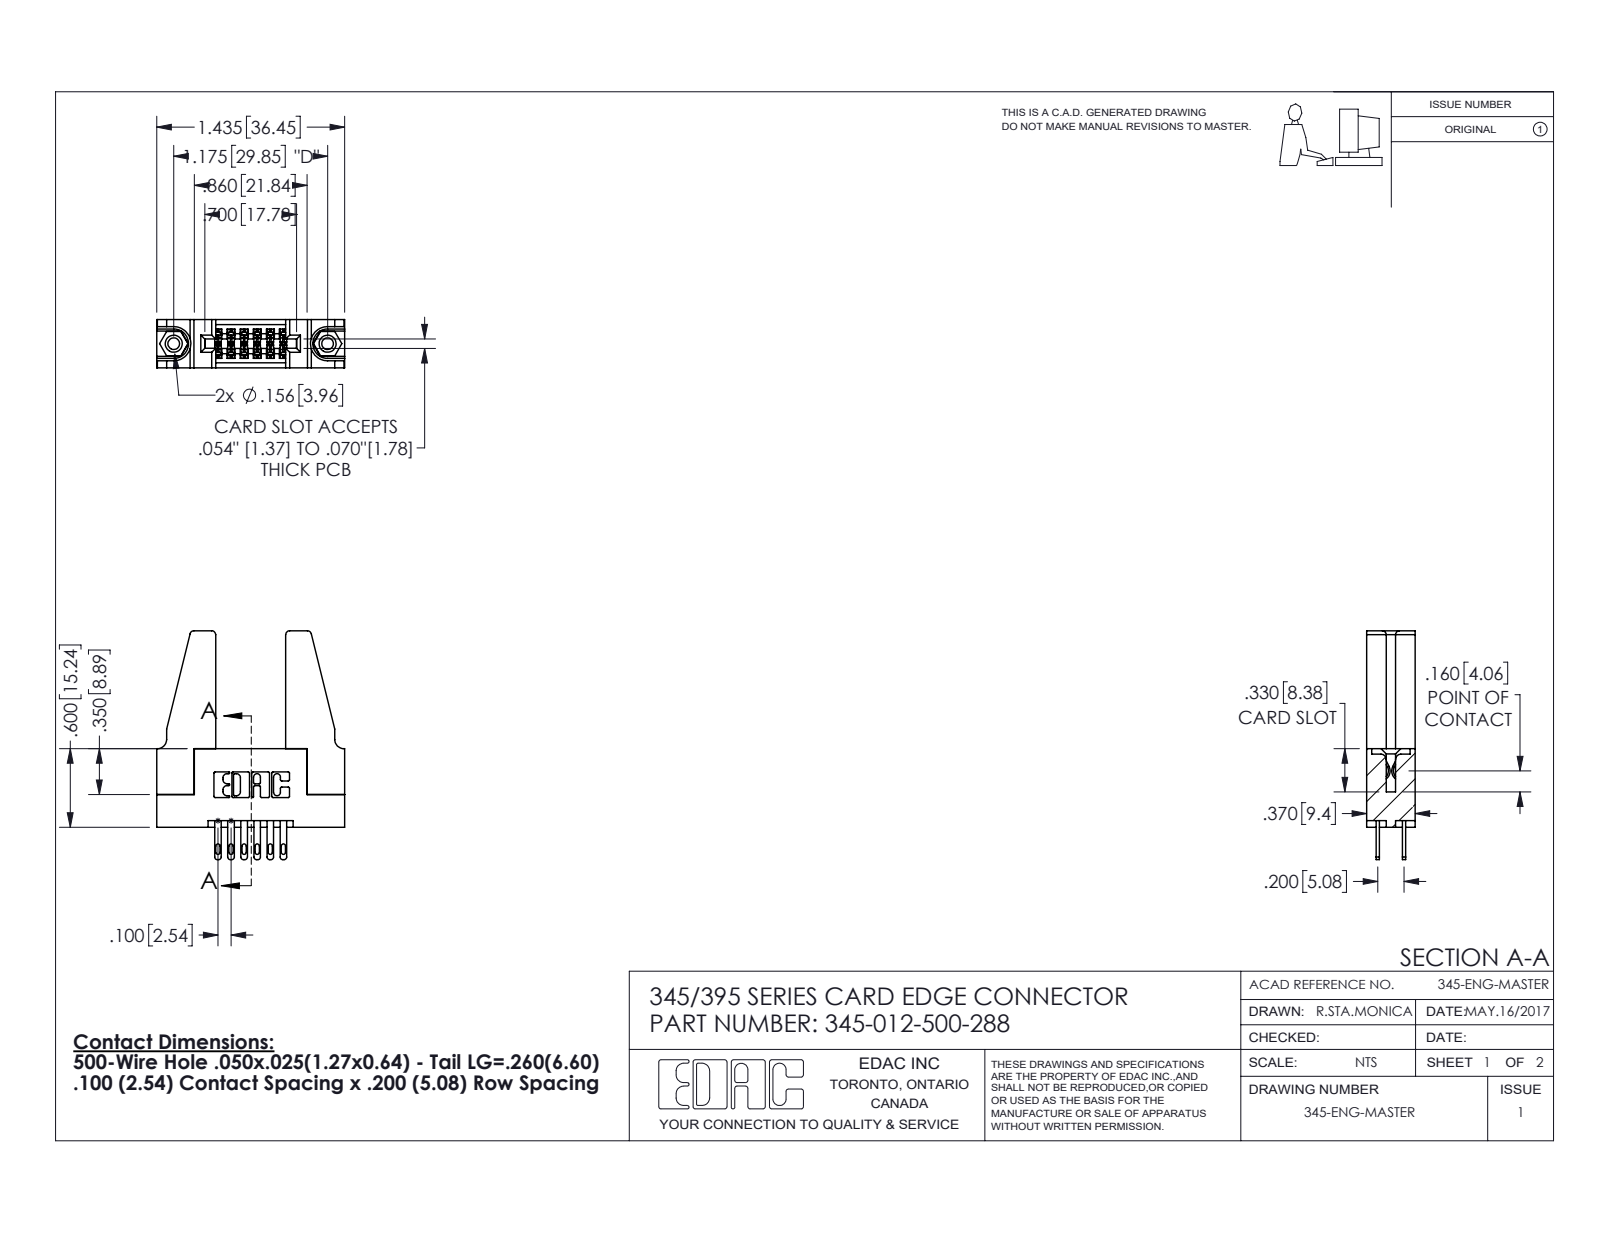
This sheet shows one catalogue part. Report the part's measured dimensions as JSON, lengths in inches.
{"part_name": "345-250-001_345-250-001-102; 345 Part_Flush Mounting Lugs - 0.156 Dia-TH; 345-220-078_345-220-088; 345-292-001_345-293-100 (+1 more)", "step_written_by": "SolidWorks 2016 (CONFIG_CONTROL_DESIGN)", "units": "inches", "bodies": {"solids": 17, "faces": 802, "planar": 476, "cylindrical": 310, "other": 16}, "overall_size": [1.747, 1.436, 0.37], "volume_in3": 0.397, "surface_area_in2": 11.38, "round_holes": [[0.089, 2], [0.125, 2], [0.156, 2], [0.064, 1]], "round_bosses_or_shafts": [[0.155, 2]], "partial_cylinders_radius": [[0.01, 22], [0.006, 18], [0.016, 12], [0.02, 12], [0.03, 8], [0.007, 6], [0.031, 6], [0.026, 3]], "face_to_face_distances": [0.37, 0.072, 0.2, 0.298, 0.098, 0.272, 0.025, 0.225, 0.698, 0.15], "hole_center_spacings": [0.27, 0.946, 1.175]}
